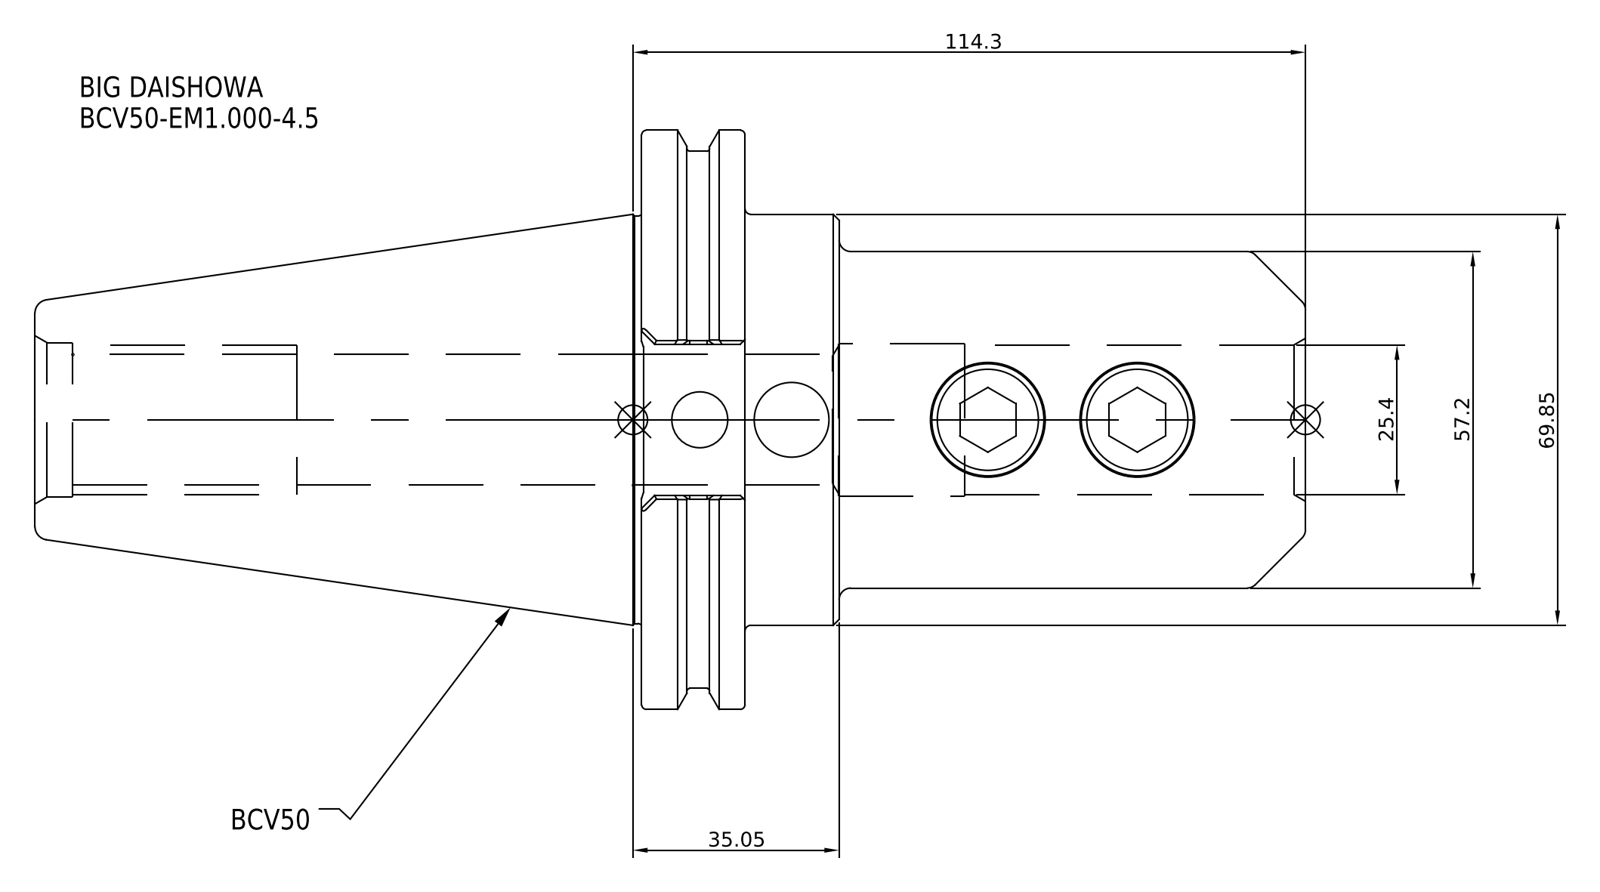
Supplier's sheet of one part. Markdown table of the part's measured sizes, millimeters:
| quantity | value |
| --- | --- |
| part name | BCV50-EM1_000-4_5 |
| STEP written by | SolidWorks 2021 (CONFIG_CONTROL_DESIGN) |
| units | millimeters |
| bodies | 1 solid, 30 faces (8 planar, 14 cylindrical, 8 other) |
| overall size | 215.9 × 98.43 × 98.43 |
| volume | 599 513 mm³ |
| surface area | 60 483 mm² |
| round holes (diameter × count) | 25.4 × 1 |
| round bosses / shafts (diameter × count) | 98.43 × 1, 91.29 × 1, 69.85 × 1, 57.2 × 1 |
| main face-to-face distances | 17.55, 16, 33.55, 136.65, 120.65, 103.1, 79.25, 95.25, 112.8, 215.9 |
